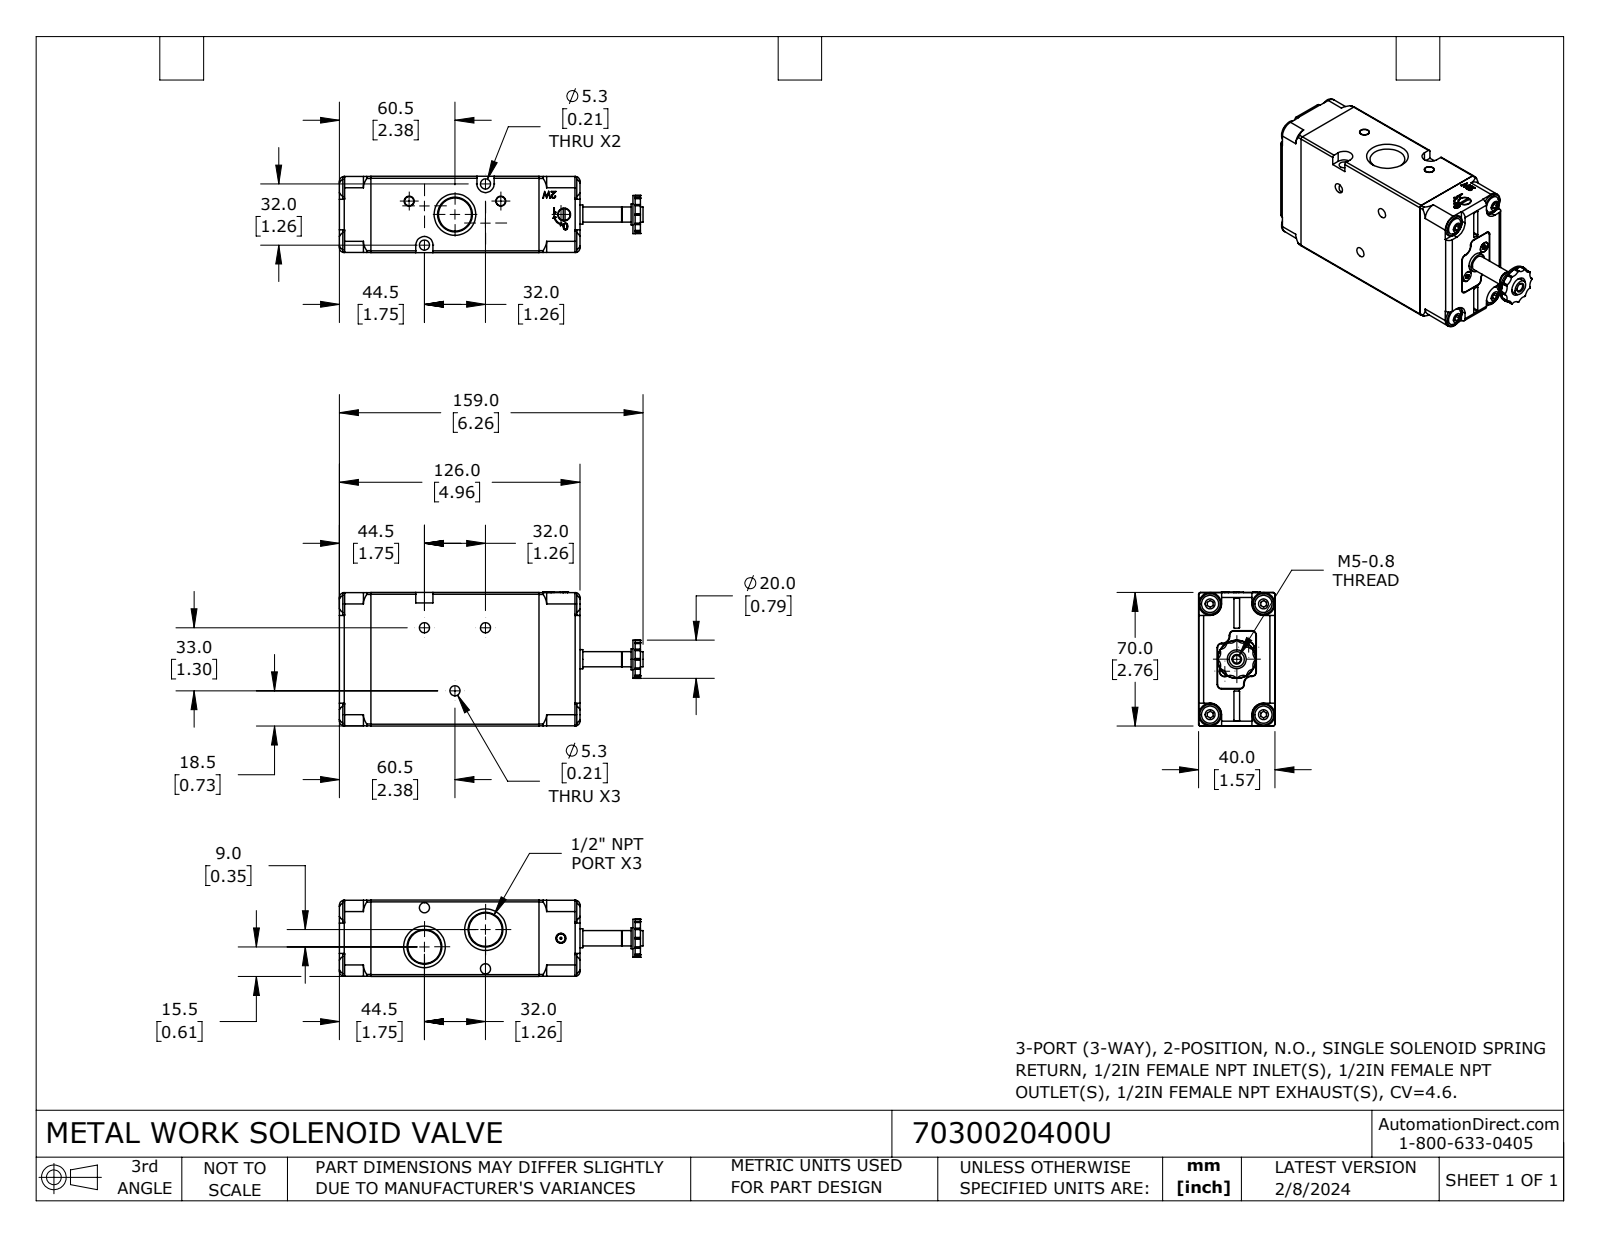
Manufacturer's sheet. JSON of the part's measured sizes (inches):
{"part_name": "7030020400U", "step_written_by": "SolidWorks 2023 (CONFIG_CONTROL_DESIGN)", "units": "inches", "bodies": {"solids": 3, "faces": 579, "planar": 253, "cylindrical": 240, "other": 86}, "overall_size": [6.26, 2.764, 1.575], "volume_in3": 20.31, "surface_area_in2": 83.18, "round_holes": [[0.209, 5], [0.228, 2], [0.163, 1], [0.264, 1], [0.402, 1], [0.591, 1]], "round_bosses_or_shafts": [[0.217, 2], [0.189, 2], [0.787, 1], [0.783, 1], [0.433, 1], [0.394, 1], [0.313, 1], [0.299, 1]], "partial_cylinders_radius": [[0.008, 12], [0.01, 12], [0.02, 12], [0.148, 12], [0.012, 8], [0.039, 8], [0.098, 8], [0.079, 6]], "face_to_face_distances": [1.575, 3.465, 1.571, 2.756, 0.846, 1.567, 2.752, 0.65, 4.114, 4.961], "hole_center_spacings": [0.348, 1.444, 0.696, 1.26, 1.74, 1.781, 2.95]}
